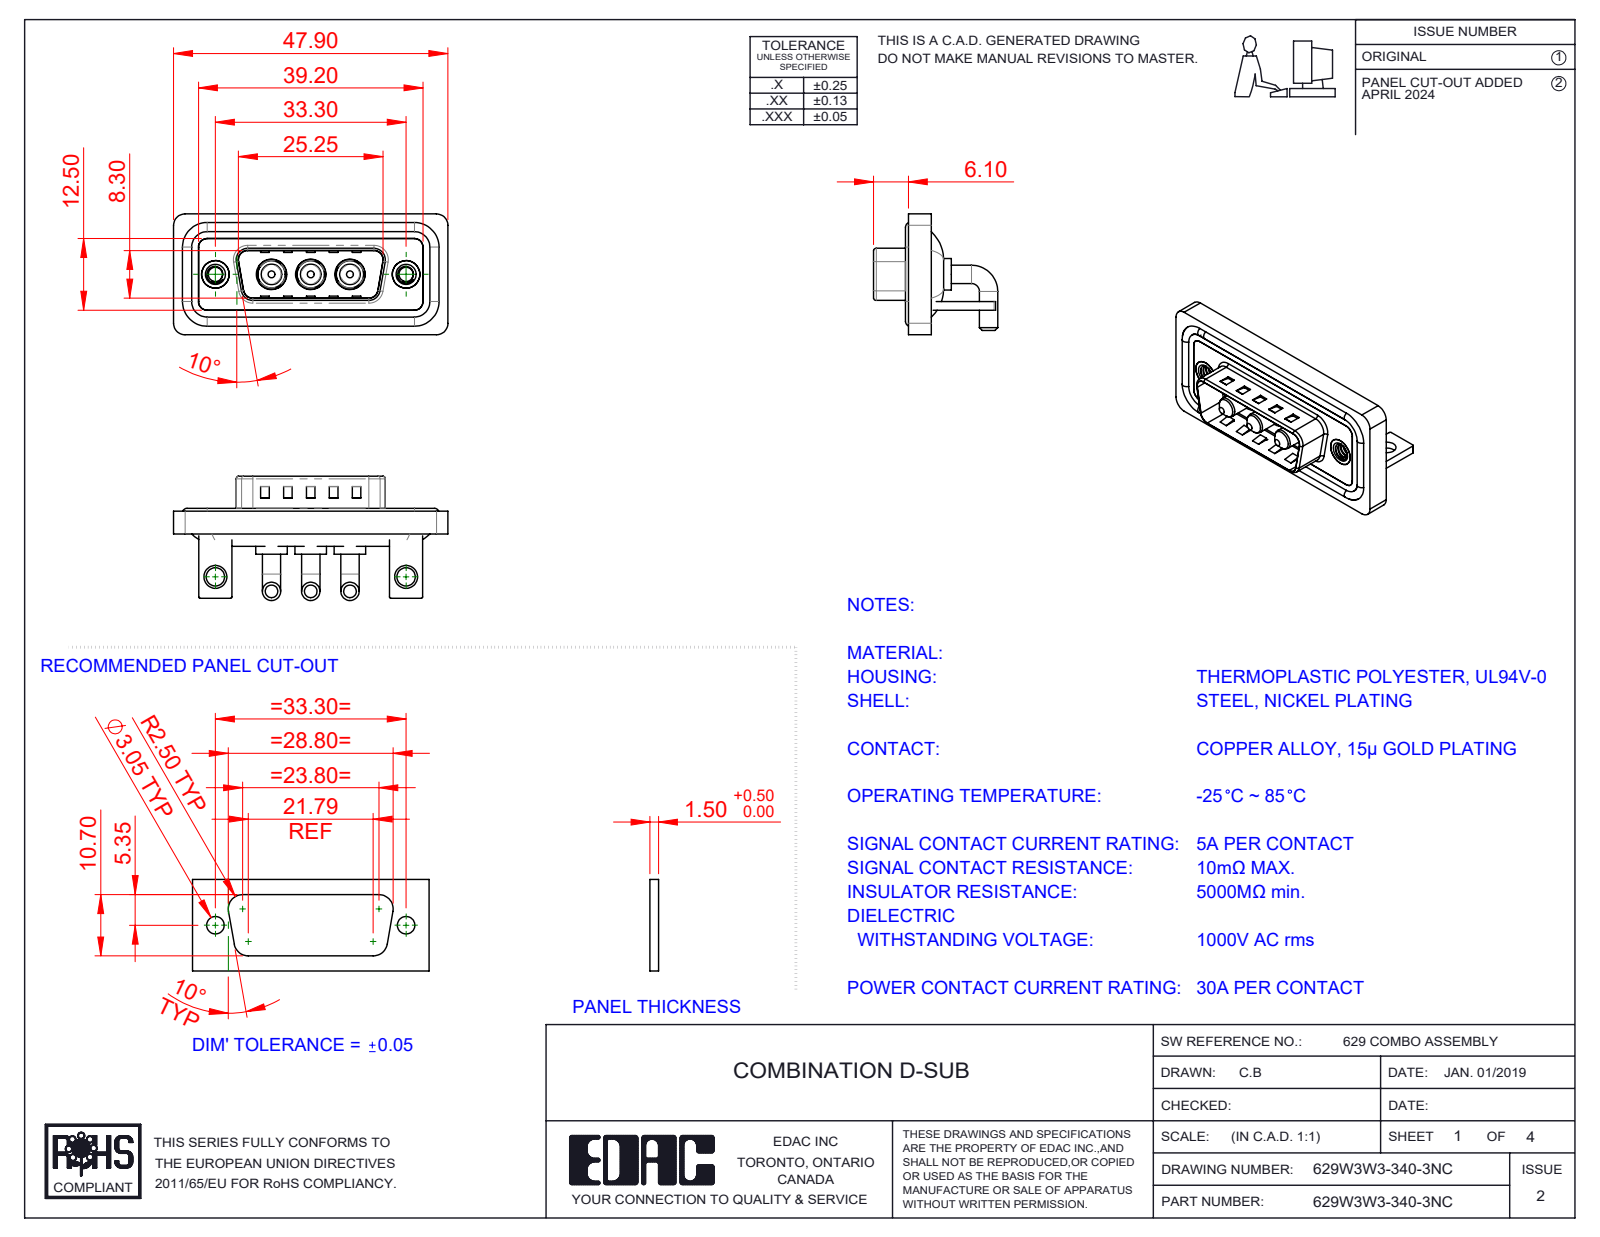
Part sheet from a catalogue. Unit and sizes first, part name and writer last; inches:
Units: inches
Overall size (bounding box): 1.886 × 0.854 × 0.831
Round holes (diameter × count): ⌀0.191 ×3, ⌀0.209 ×3, ⌀0.098 ×2, ⌀0.126 ×2, ⌀0.157 ×2, ⌀0.189 ×2, ⌀0.197 ×2
Round bosses / shafts (diameter × count): ⌀0.126 ×6, ⌀0.063 ×4, ⌀0.217 ×3, ⌀0.205 ×3, ⌀0.187 ×3, ⌀0.148 ×3, ⌀0.142 ×3, ⌀0.193 ×2
Partial cylindrical surfaces — rounded edges, fillets, slot ends (radius × count): R0.079 ×21, R0.059 ×18, R0.01 ×16, R0.02 ×9, R0.063 ×8, R0.024 ×4, R0.026 ×4, R0.035 ×4
Main face-to-face distances: 0.016, 0.059, 0.031, 0.114, 0.043, 0.083, 0.146, 0.063, 0.047, 0.177
Hole centre spacings: 0.27, 0.386, 0.656, 0.925, 1.311, 0.539
Volume: 0.374 in³ · Surface area: 15 in²
Bodies: 15 solids, 614 faces (227 planar, 265 cylindrical, 122 other)
Part name (STEP PRODUCT): 629Combo Housing_3W3; 629Combo Waterproof Housing_15 Contacts; 629Combo Stabilizer Bracket; 629Combo Threaded Rivet_B (+4 more)
STEP written by: SolidWorks 2023 (CONFIG_CONTROL_DESIGN)
